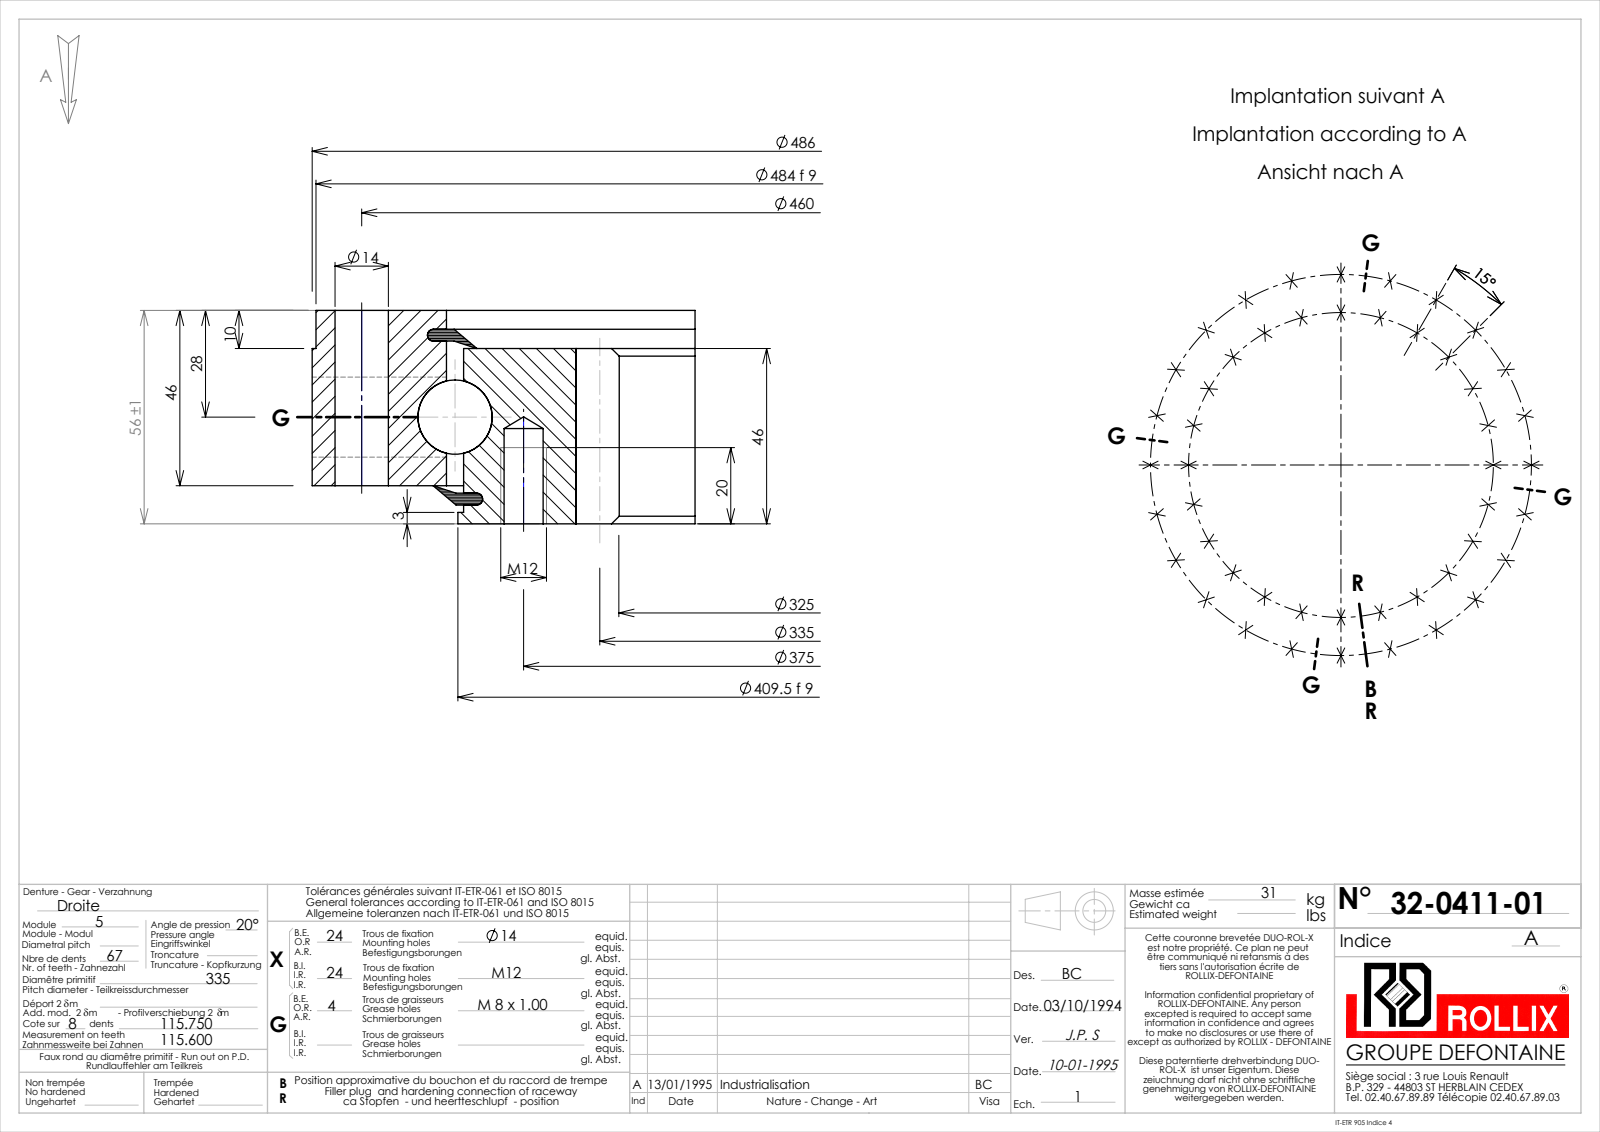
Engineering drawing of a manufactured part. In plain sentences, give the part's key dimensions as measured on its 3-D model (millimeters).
The part is named "32-0411-01". Its 3-D file was written by "SolidWorks 2016 (CONFIG_CONTROL_DESIGN)". It is 9 solids with 704 faces: 188 planar, 265 cylindrical and 251 other. Overall it measures 501.3 by 501.3 by 56 millimeters. Its volume is 3 730 000 cubic millimeters and its surface area 654 078 square millimeters. Round holes: 24 of diameter 10.25, 24 of diameter 14, 4 of diameter 7, 1 of diameter 415.5. Round bosses or shafts: 4 of diameter 8, 1 of diameter 486, 1 of diameter 484, 1 of diameter 409.5, 1 of diameter 406.5. Partial cylindrical surfaces (rounded edges, fillets, slot ends): 1 of radius 162.5, 1 of radius 173.75. The main face-to-face distances are 46, 10, 36, 56, 1.95, 5.05, 43, 4.95, 8.05, 47.95. The hole center spacings are 48.95, 187.5, 324.76, 346.45, 362.22, 371.79, 97.06, 143.5.
